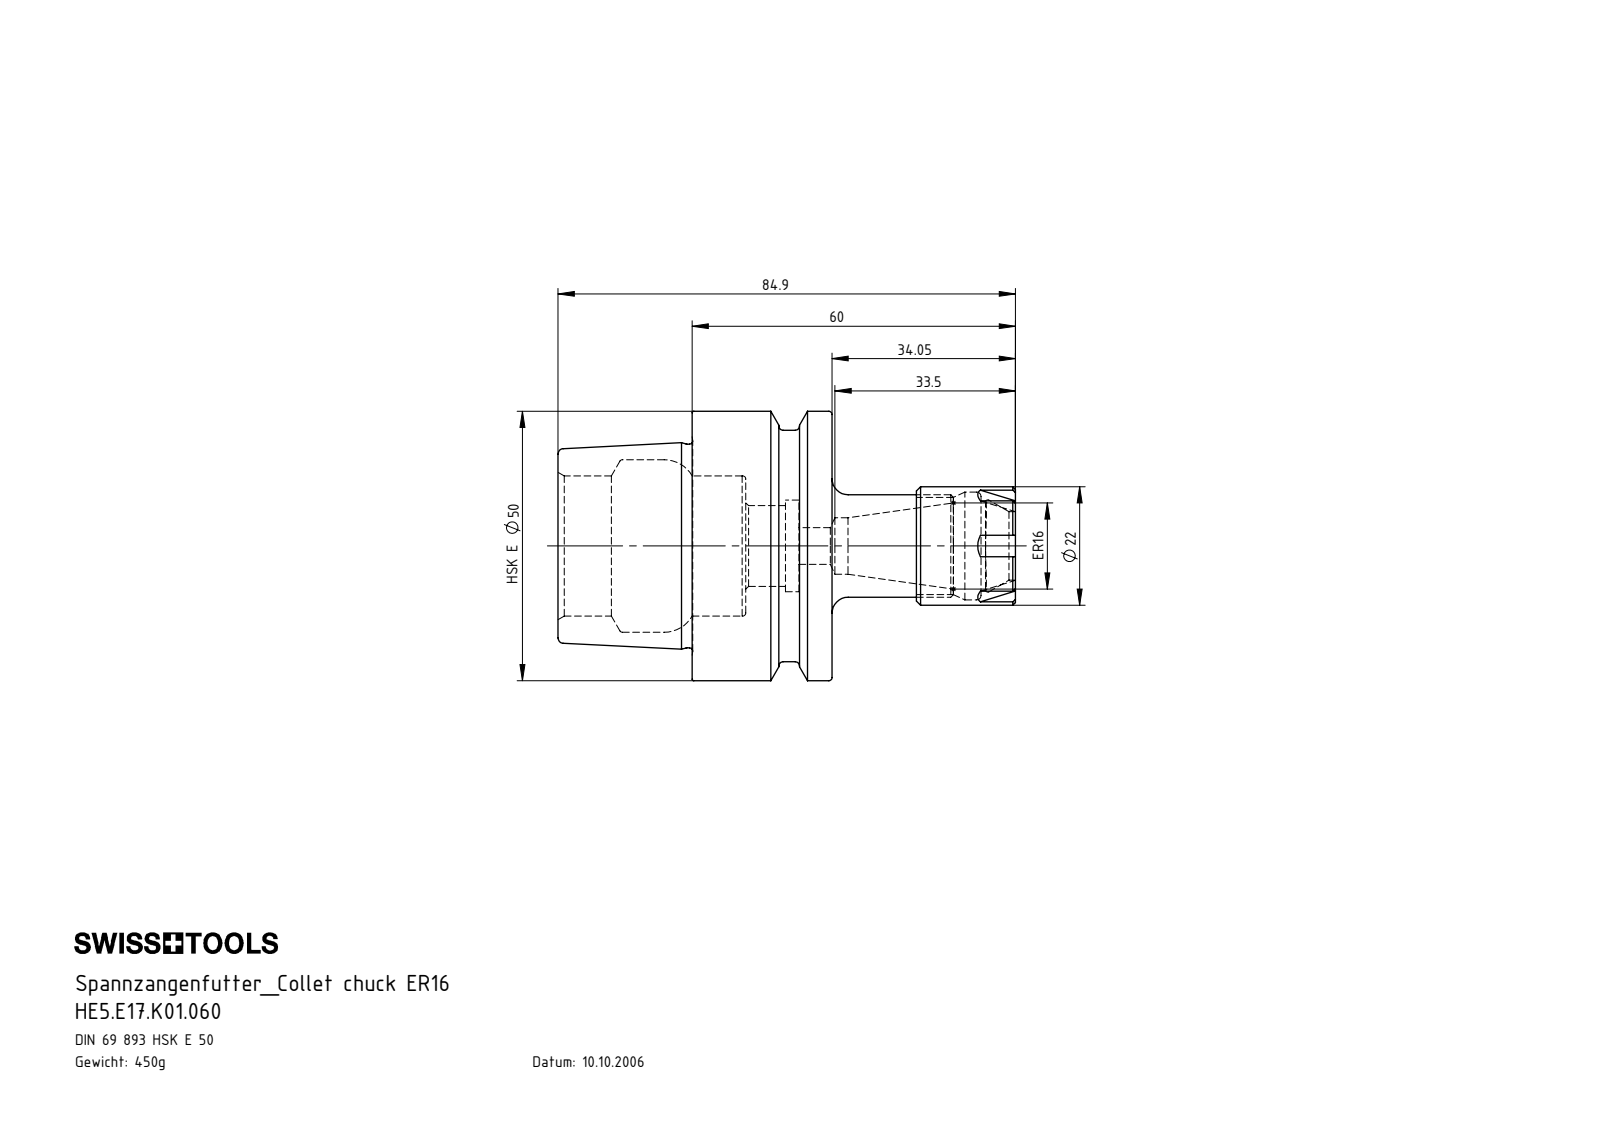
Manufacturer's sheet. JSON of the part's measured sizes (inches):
{"part_name": "E17-ER1.001.018; HE5.E17.K01.060; HE5-E17.K01.060_A_Fertigbearbeitung", "step_written_by": "SolidWorks 2017 (CONFIG_CONTROL_DESIGN)", "units": "inches", "bodies": {"solids": 2, "faces": 131, "planar": 33, "cylindrical": 35, "other": 63}, "overall_size": [3.343, 1.969, 1.969], "volume_in3": 3.5, "surface_area_in2": 30.89, "round_holes": [[0.268, 1], [0.413, 1], [0.5, 1], [0.591, 1], [0.669, 1], [0.709, 1], [0.787, 1], [1.024, 1], [1.26, 1]], "round_bosses_or_shafts": [[1.969, 1], [1.691, 1], [1.489, 1], [0.866, 1], [0.748, 1]], "partial_cylinders_radius": [[0.303, 2]], "face_to_face_distances": [1.022, 0.98, 2.002, 1.372, 0.392, 0.63, 1.76, 0.78, 0.388, 0.242]}
